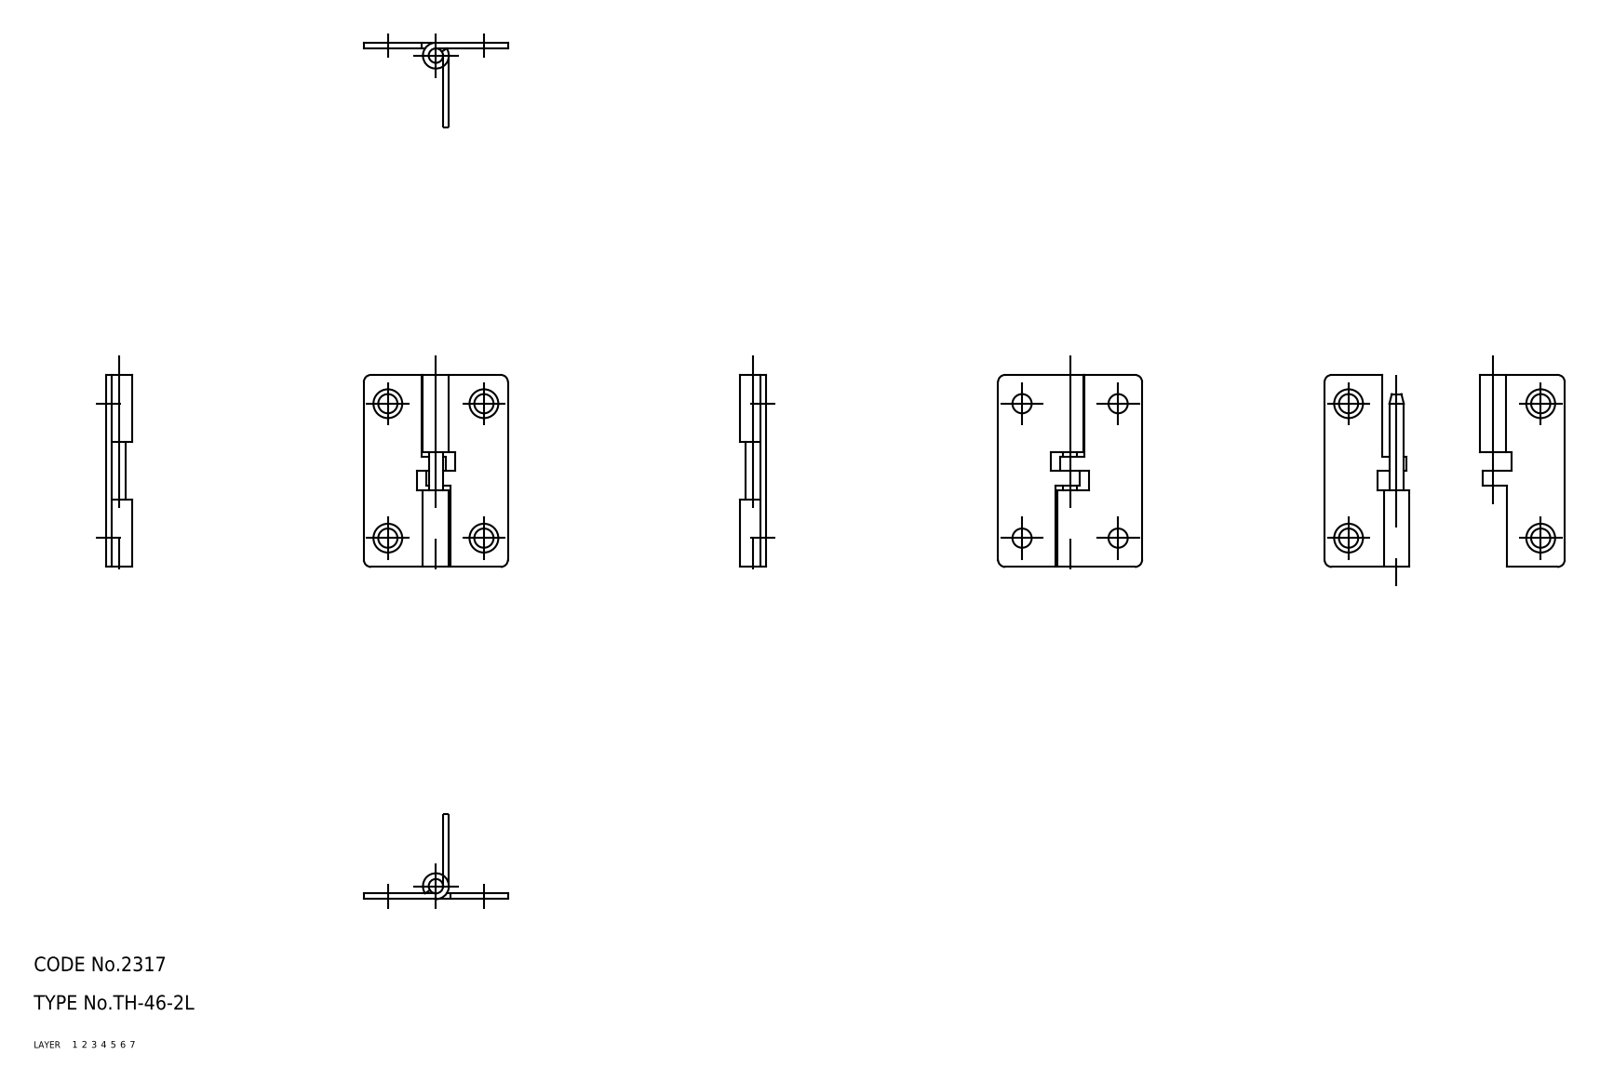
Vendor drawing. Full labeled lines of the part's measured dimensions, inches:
Part name (STEP PRODUCT): shaft; hinge piece_B; hinge piece_A; TH_46_2L_9542_36
STEP written by: CADfix (AUTOMOTIVE_DESIGN)
Units: inches
Bodies: 3 solids, 54 faces (0 planar, 0 cylindrical, 54 other)
Overall size (bounding box): 1.575 × 1.181 × 0.213
Volume: 0.115 in³ · Surface area: 5.405 in²
